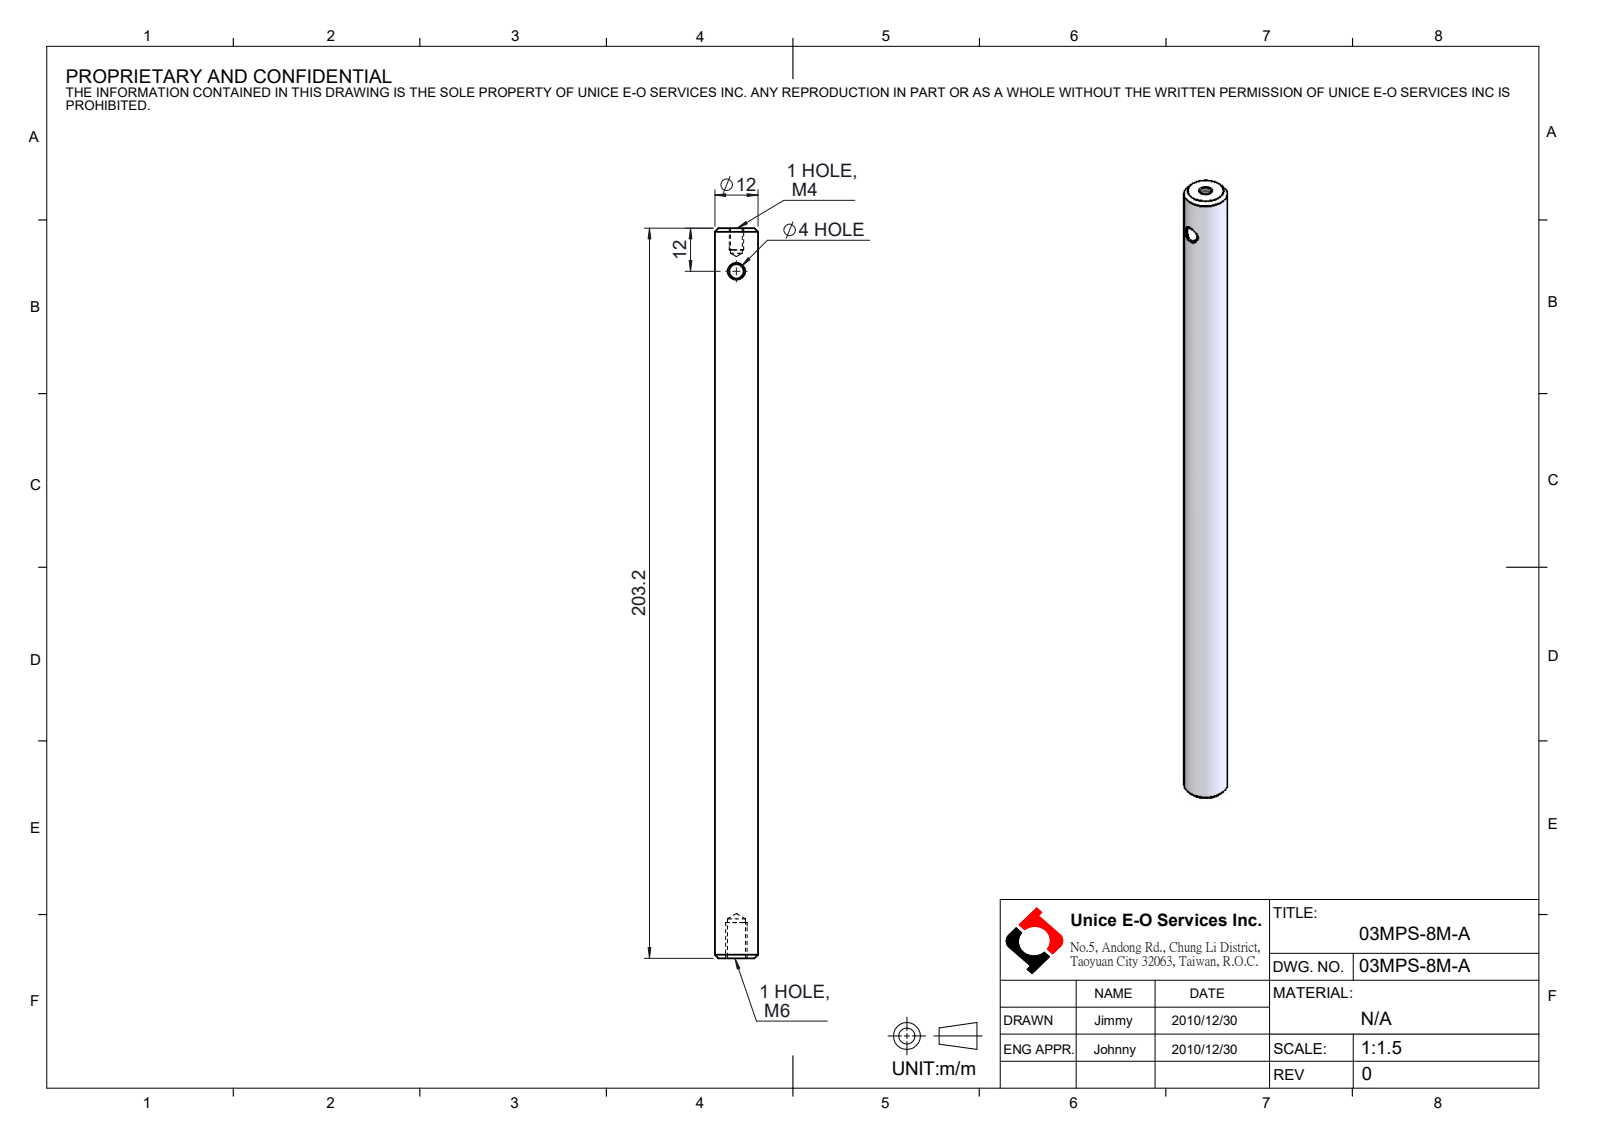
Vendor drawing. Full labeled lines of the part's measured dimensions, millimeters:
Part name (STEP PRODUCT): 03MPS-8M-A
STEP written by: SolidWorks 2016 (CONFIG_CONTROL_DESIGN)
Units: millimetres
Bodies: 1 solid, 22 faces (2 planar, 8 cylindrical, 12 other)
Overall size (bounding box): 203.2 × 12 × 12
Volume: 22 507 mm³ · Surface area: 8 204 mm²
Round holes (diameter × count): ⌀3.3 ×1, ⌀4 ×1, ⌀5 ×1
Round bosses / shafts (diameter × count): ⌀12 ×1
Main face-to-face distances: 203.2
